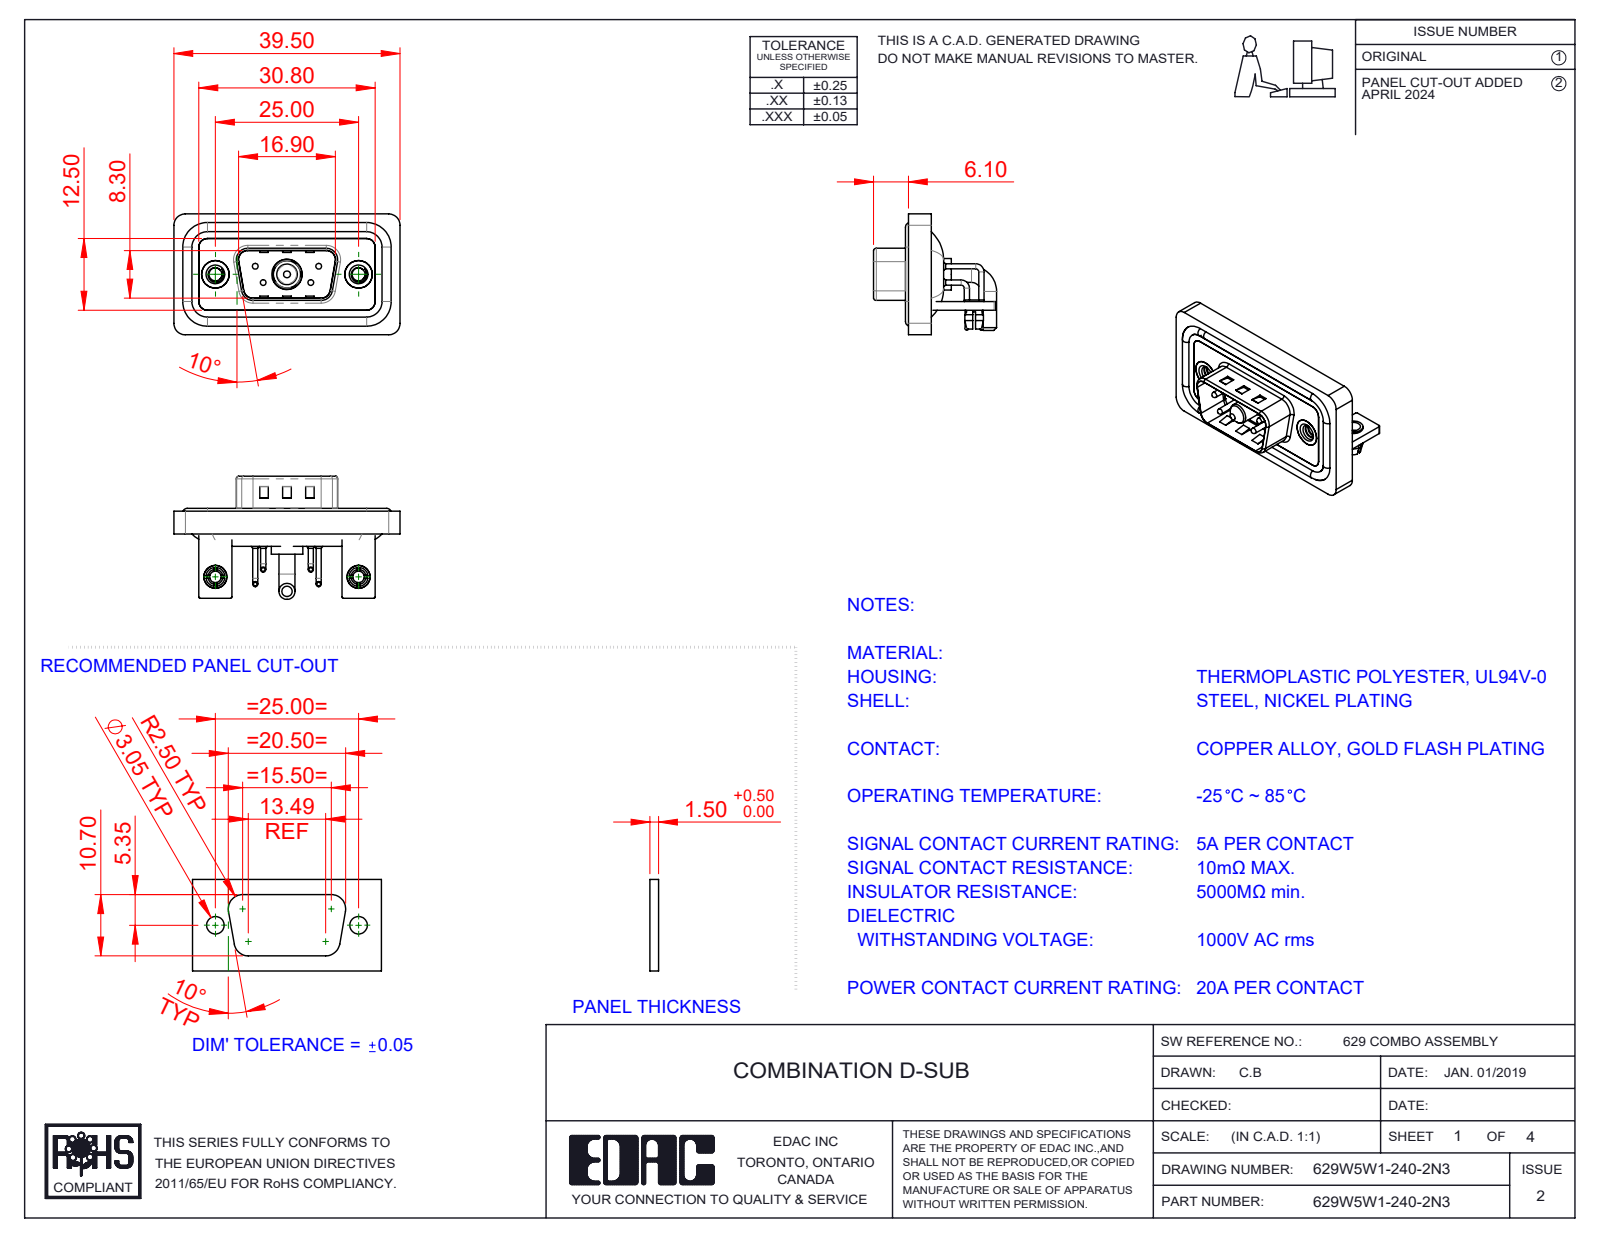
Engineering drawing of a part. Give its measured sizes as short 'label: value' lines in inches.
name: 629Combo Board Lock; 629W5W1-140-2N3; Power Pin_20A RA; 629Combo Contact Row 1 (+7 more)
written by: SolidWorks 2023 (CONFIG_CONTROL_DESIGN)
unit: in
bodies: 17 solids, 1026 faces (479 planar, 395 cylindrical, 152 other)
size: 1.555 × 0.846 × 0.831
volume: 0.292 in³; area: 12.34 in²
holes: 6× ⌀0.079, 4× ⌀0.03, 4× ⌀0.063, 2× ⌀0.089, 2× ⌀0.098, 2× ⌀0.126, 2× ⌀0.157, 2× ⌀0.189, 2× ⌀0.197, 1× ⌀0.191, 1× ⌀0.209
bosses: 8× ⌀0.035, 4× ⌀0.063, 4× ⌀0.059, 4× ⌀0.039, 4× ⌀0.026, 2× ⌀0.193, 2× ⌀0.157, 2× ⌀0.134
rounds: 19× R0.079, 18× R0.059, 16× R0.01, 9× R0.02, 8× R0.063, 4× R0.024, 4× R0.026, 4× R0.035
face distances: 0.016, 0.059, 0.031, 0.114, 0.043, 0.083, 0.047, 0.063, 0.098, 0.146
hole spacings: 0.124, 0.225, 0.28, 0.492, 0.713, 0.984, 0.173, 0.173
